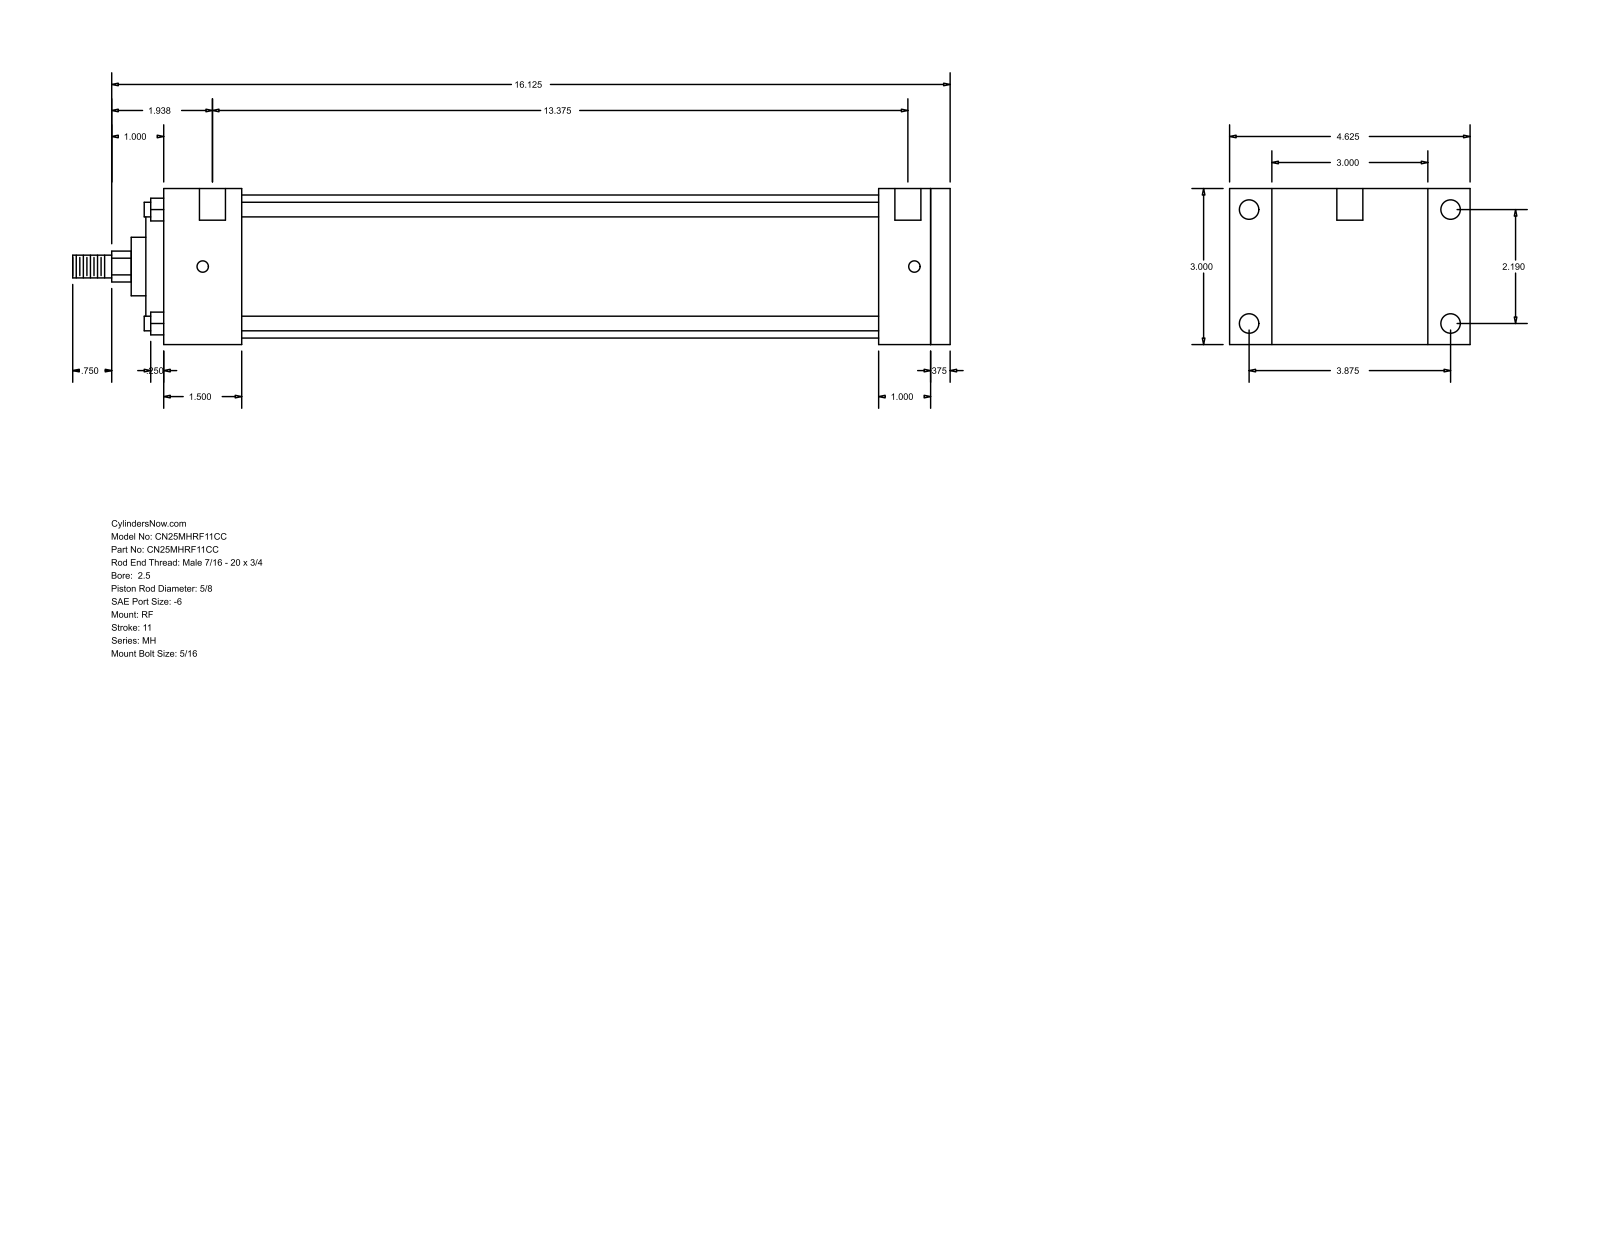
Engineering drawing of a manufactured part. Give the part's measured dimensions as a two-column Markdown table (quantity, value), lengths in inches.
| quantity | value |
| --- | --- |
| part name | MH_RF__0250_0.625 |
| STEP written by | GSSL Pune (CONFIG_CONTROL_DESIGN) |
| units | inches |
| bodies | 0 solids, 94 faces (65 planar, 29 cylindrical, 0 other) |
| overall size | 16.875 × 4.625 × 3 |
| round holes (diameter × count) | 0.219 × 4, 0.375 × 4, 0.5 × 2 |
| round bosses / shafts (diameter × count) | 0.281 × 4, 2.75 × 1, 2.187 × 1, 1.125 × 1, 0.625 × 1, 0.437 × 1 |
| partial cylindrical surfaces (radius × count) | 0.297 × 1 |
| main face-to-face distances | 3, 0.375, 15.125, 14.75, 1, 1.5, 13.75, 1.375, 12.25, 13.25 |
| hole center spacings | 2.19, 3.875, 4.451, 13.687, 0.125, 0.187, 13.375, 13.5 |
